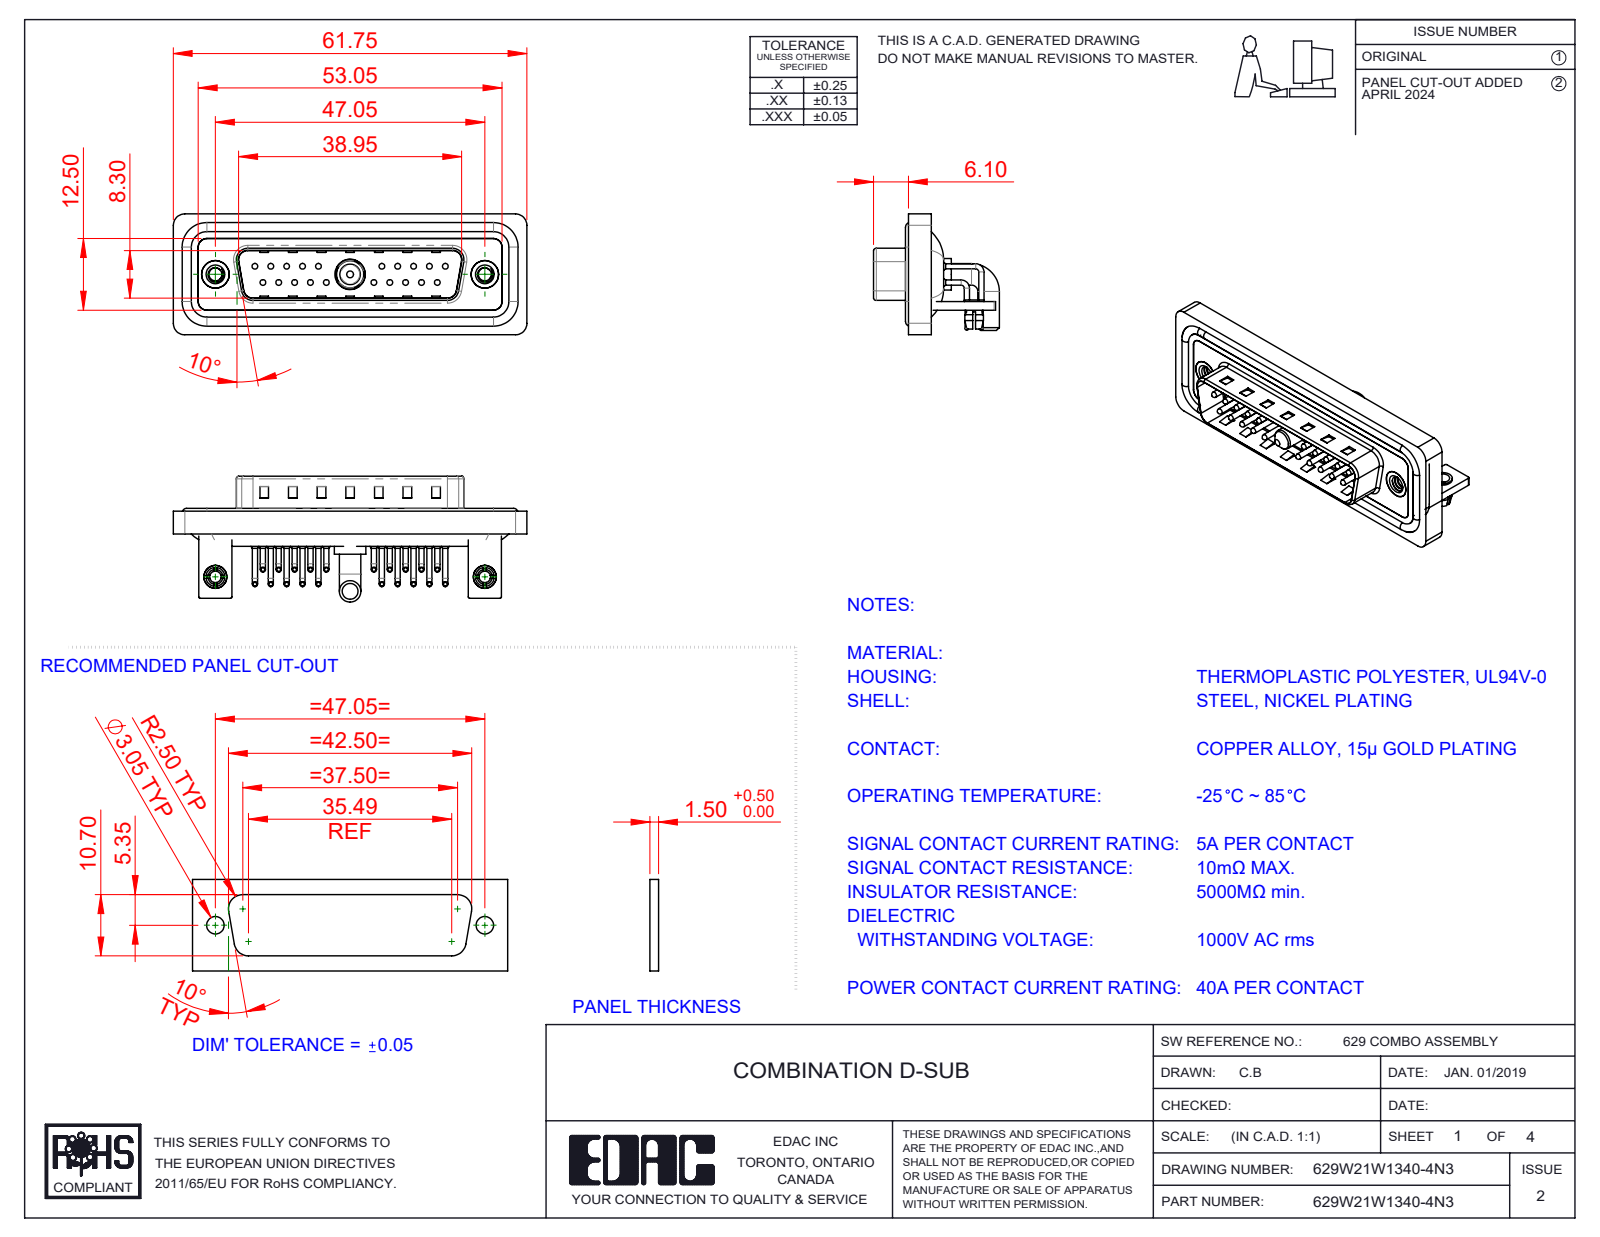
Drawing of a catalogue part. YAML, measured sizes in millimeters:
part_name: "629Combo Board Lock; 629Combo Threaded Rivet_3; 629Combo Contact Row 1; 629Combo Shell Front_25 Contacts (+7 more)"
step_written_by: "SolidWorks 2023 (CONFIG_CONTROL_DESIGN)"
units: millimeters
bodies: {solids: 33, faces: 2858, planar: 1567, cylindrical: 979, other: 312}
overall_size: [61.75, 21.98, 21.1]
volume: 7805
surface_area: 13562
round_holes:
  - {diameter: 2, count: 22}
  - {diameter: 0.75, count: 20}
  - {diameter: 1.6, count: 20}
  - {diameter: 2.26, count: 2}
  - {diameter: 2.5, count: 2}
  - {diameter: 3.2, count: 2}
  - {diameter: 4, count: 2}
  - {diameter: 4.8, count: 2}
  - {diameter: 5, count: 2}
  - {diameter: 4.85, count: 1}
  - {diameter: 5.3, count: 1}
round_bosses_or_shafts:
  - {diameter: 0.9, count: 40}
  - {diameter: 1.5, count: 20}
  - {diameter: 1, count: 20}
  - {diameter: 0.65, count: 20}
  - {diameter: 1.6, count: 4}
  - {diameter: 4.9, count: 2}
  - {diameter: 4, count: 2}
  - {diameter: 3.75, count: 2}
partial_cylinders:
  - {radius: 1.01, count: 20}
  - {radius: 2, count: 19}
  - {radius: 1.5, count: 18}
  - {radius: 0.25, count: 16}
  - {radius: 0.5, count: 9}
  - {radius: 1.6, count: 8}
  - {radius: 0.6, count: 4}
  - {radius: 0.65, count: 4}
face_to_face_distances: [0.4, 0.8, 2.1, 2.9, 1.5, 1.1, 4.1, 1.6, 4.5, 3.7]
hole_center_spacings: [3.16, 2.77, 5.54, 8.31, 5.04, 19.39, 20.97, 22.16]
